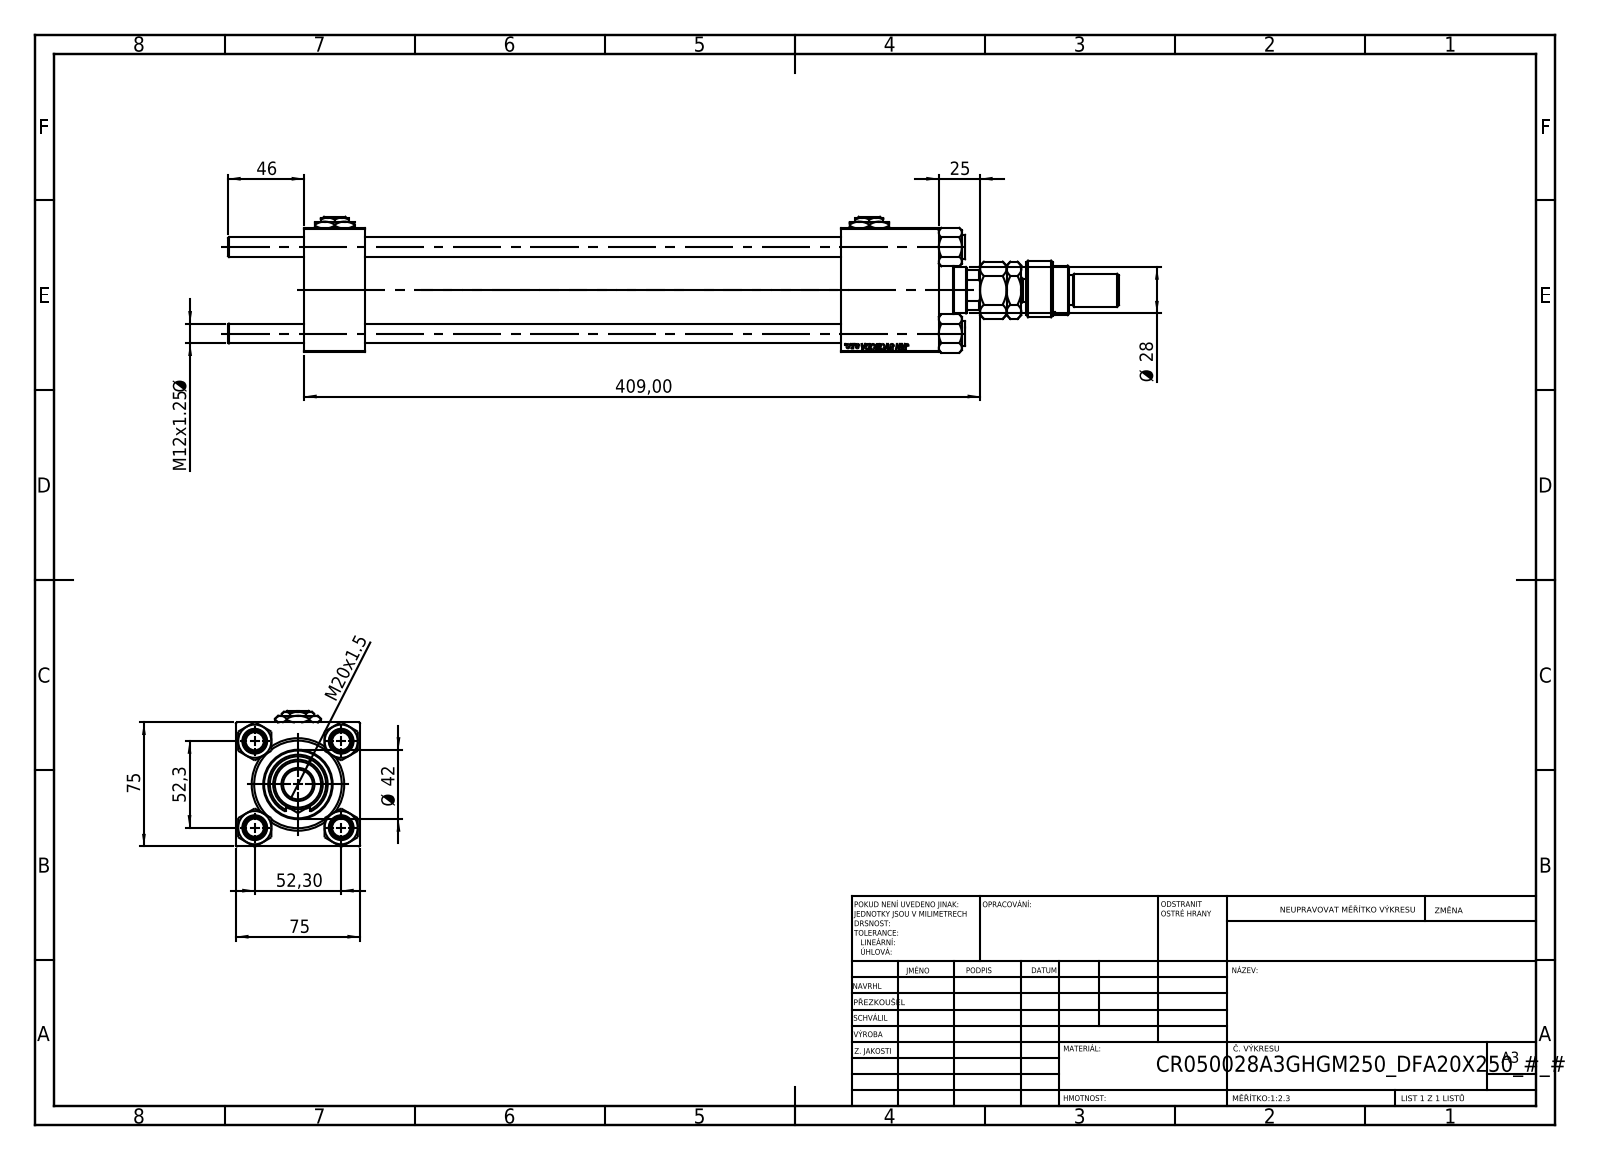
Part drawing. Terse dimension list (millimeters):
name: MFA; V215CR_BODY_A; CR025_012_A_0_G_A_G_M_020_+#_##_TYCINKA; V215_VC_A (+4 more)
written by: SolidWorks 2019 (CONFIG_CONTROL_DESIGN)
unit: mm
bodies: 15 solids, 1318 faces (595 planar, 101 cylindrical, 622 other)
size: 539 × 82.27 × 75
volume: 1 107 000 mm³; area: 316 616 mm²
holes: 4× ⌀12, 2× ⌀7, 2× ⌀20.96, 2× ⌀30, 1× ⌀18.5, 1× ⌀28, 1× ⌀31, 1× ⌀41, 1× ⌀50, 1× ⌀53
bosses: 4× ⌀15, 1× ⌀56, 1× ⌀42, 1× ⌀36, 1× ⌀30, 1× ⌀22, 1× ⌀20, 1× ⌀18
rounds: 1× R7.5, 1× R12, 1× R13.5
face distances: 75, 37, 384, 347, 325, 59, 288, 355.3, 318.3, 30.3
hole spacings: 36.98, 52.3, 73.96, 323.5
